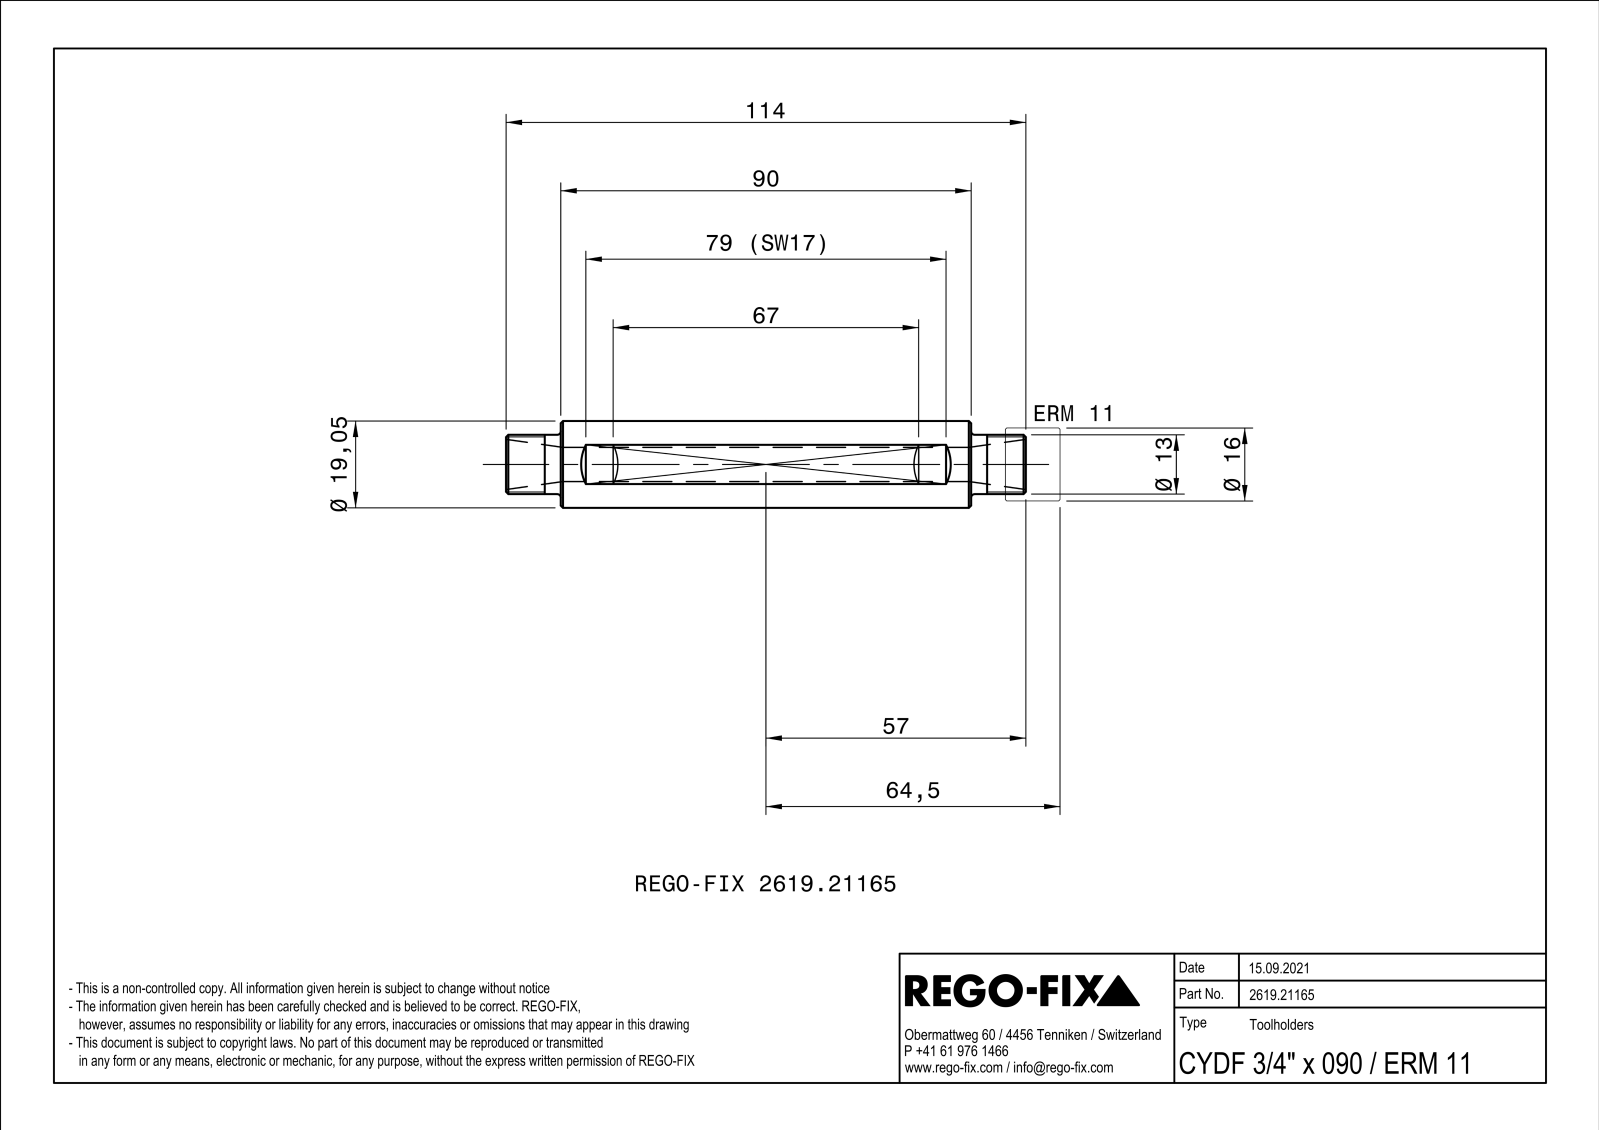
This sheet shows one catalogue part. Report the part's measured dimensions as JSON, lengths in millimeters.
{"part_name": "NOCUT", "step_written_by": "SIEMENS PLM Software Solid Edge ST10 (AUTOMOTIVE_DESIGN)", "units": "millimeters", "bodies": {"solids": 1, "faces": 29, "planar": 13, "cylindrical": 6, "other": 10}, "overall_size": [114, 19.05, 19.05], "volume_mm3": 22639, "surface_area_mm2": 9467, "round_holes": [[7.5, 1]], "round_bosses_or_shafts": [[19.05, 1], [13, 1]], "face_to_face_distances": [17, 90, 12, 102, 7.77, 51.61, 43.84, 114]}
